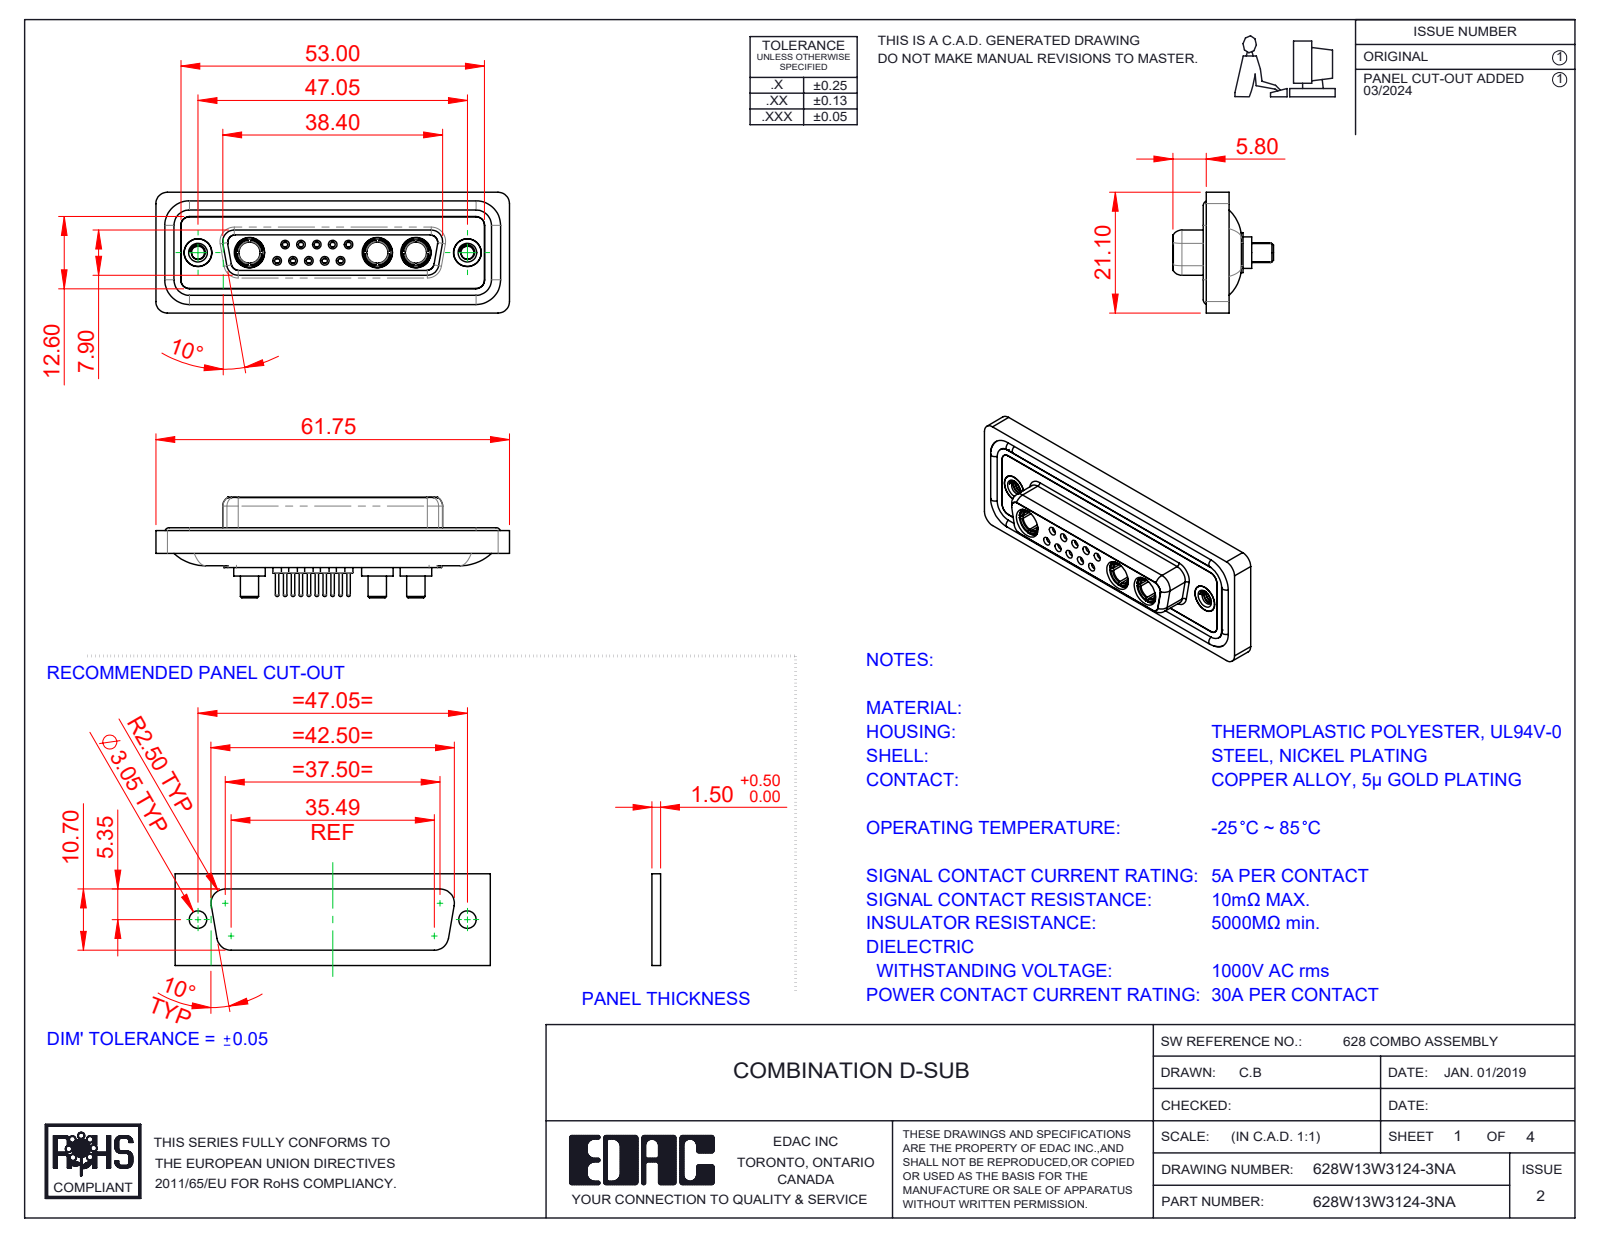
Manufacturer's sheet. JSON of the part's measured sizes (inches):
{"part_name": "Power Socket_30A S; 628Combo Housing_13W3; 628Combo Shell Front_25 Contacts; 628W13W3124-3NA (+5 more)", "step_written_by": "SolidWorks 2023 (CONFIG_CONTROL_DESIGN)", "units": "inches", "bodies": {"solids": 23, "faces": 1156, "planar": 342, "cylindrical": 449, "other": 365}, "overall_size": [2.431, 0.831, 0.691], "volume_in3": 0.506, "surface_area_in2": 21.27, "round_holes": [[0.035, 10], [0.043, 10], [0.059, 10], [0.079, 10], [0.063, 5], [0.067, 5], [0.191, 5], [0.146, 3], [0.209, 3], [0.089, 2], [0.157, 2], [0.159, 2]], "round_bosses_or_shafts": [[0.087, 10], [0.024, 10], [0.063, 9], [0.217, 3], [0.205, 3], [0.195, 3], [0.187, 3], [0.148, 3]], "partial_cylinders_radius": [[0.059, 22], [0.079, 18], [0.053, 8], [0.063, 8], [0.01, 4], [0.02, 4], [0.024, 4], [0.026, 4]], "face_to_face_distances": [0.016, 0.071, 0.293, 0.222, 0.02, 0.26, 0.278, 0.063, 0.114, 0.043], "hole_center_spacings": [0.124, 0.109, 0.198, 0.198, 0.218, 0.327, 0.295, 0.109]}
